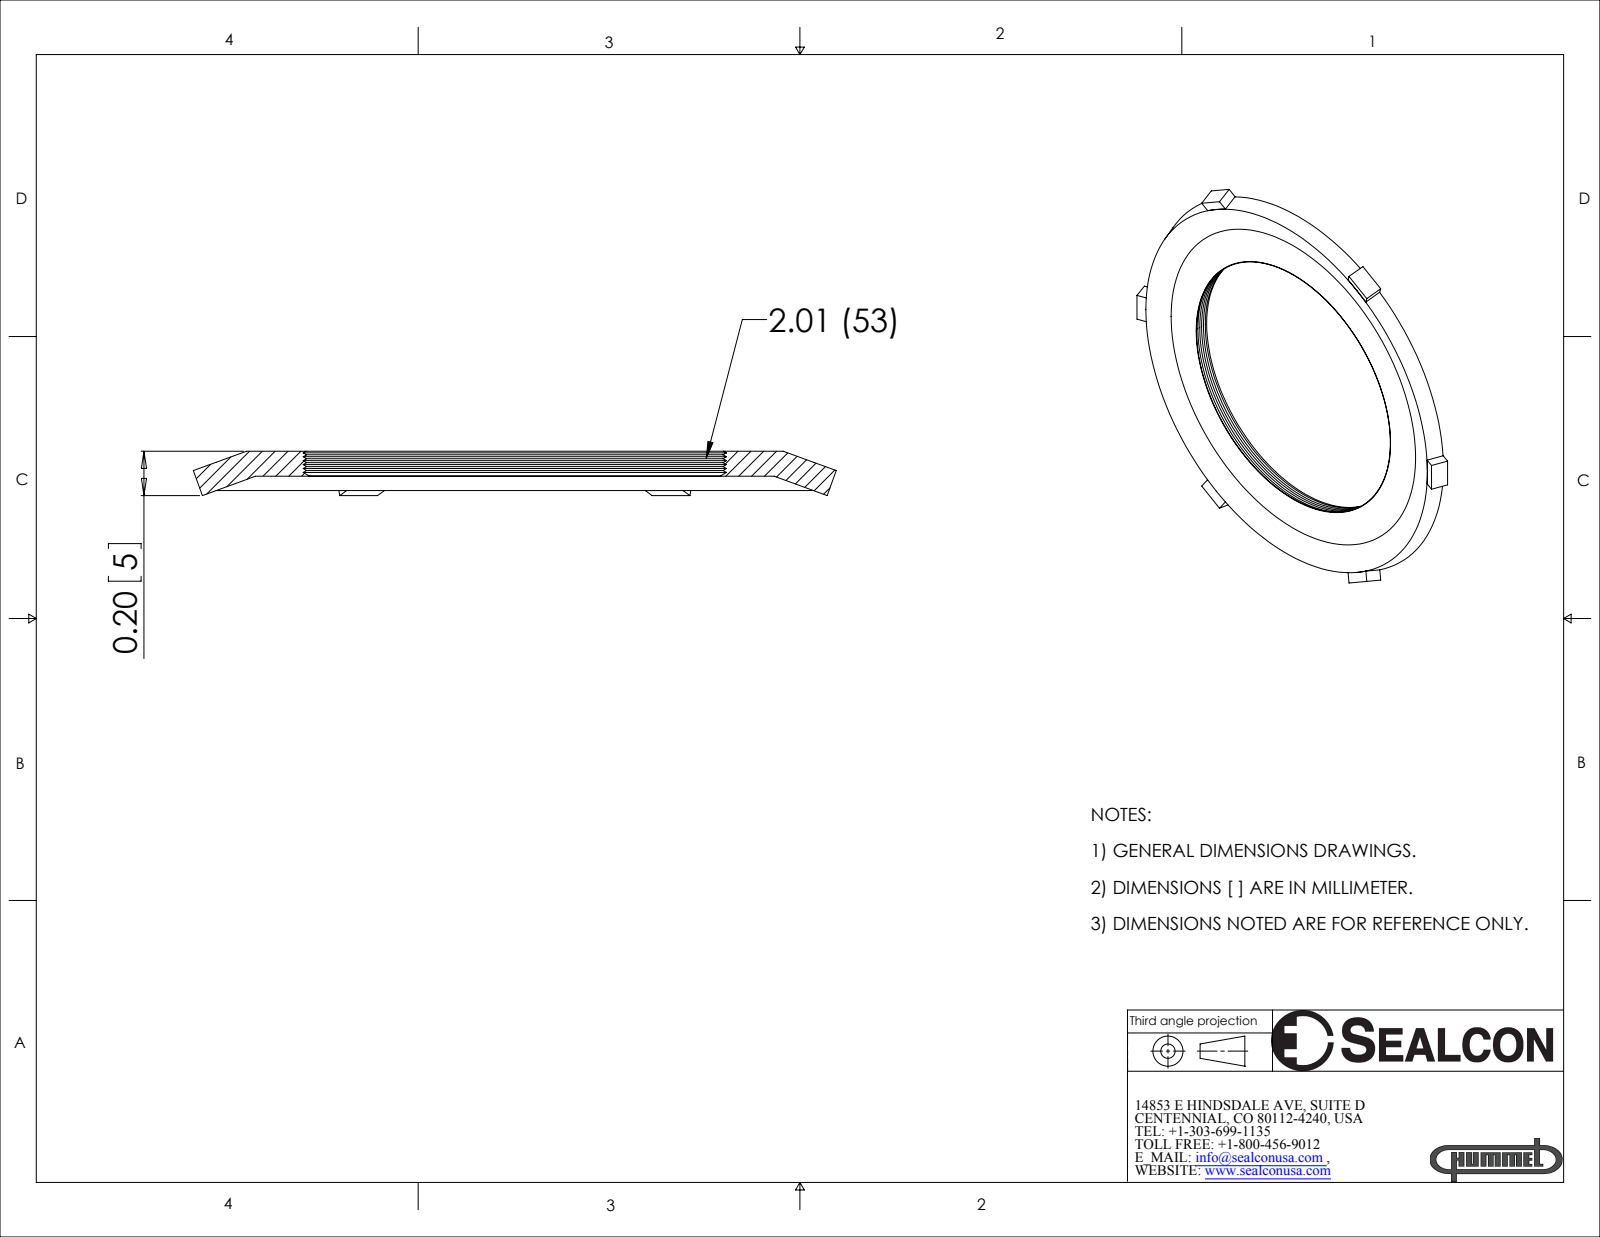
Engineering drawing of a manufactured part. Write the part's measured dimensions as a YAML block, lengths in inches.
part_name: "NN-34-ST"
step_written_by: "SolidWorks 2008 (CONFIG_CONTROL_DESIGN)"
units: inches
bodies: {solids: 1, faces: 80, planar: 44, cylindrical: 0, other: 36}
overall_size: [2.947, 2.82, 0.203]
volume: 0.394
surface_area: 9.353
face_to_face_distances: [0.115, 0.122, 0.2, 0.122, 0.11]
